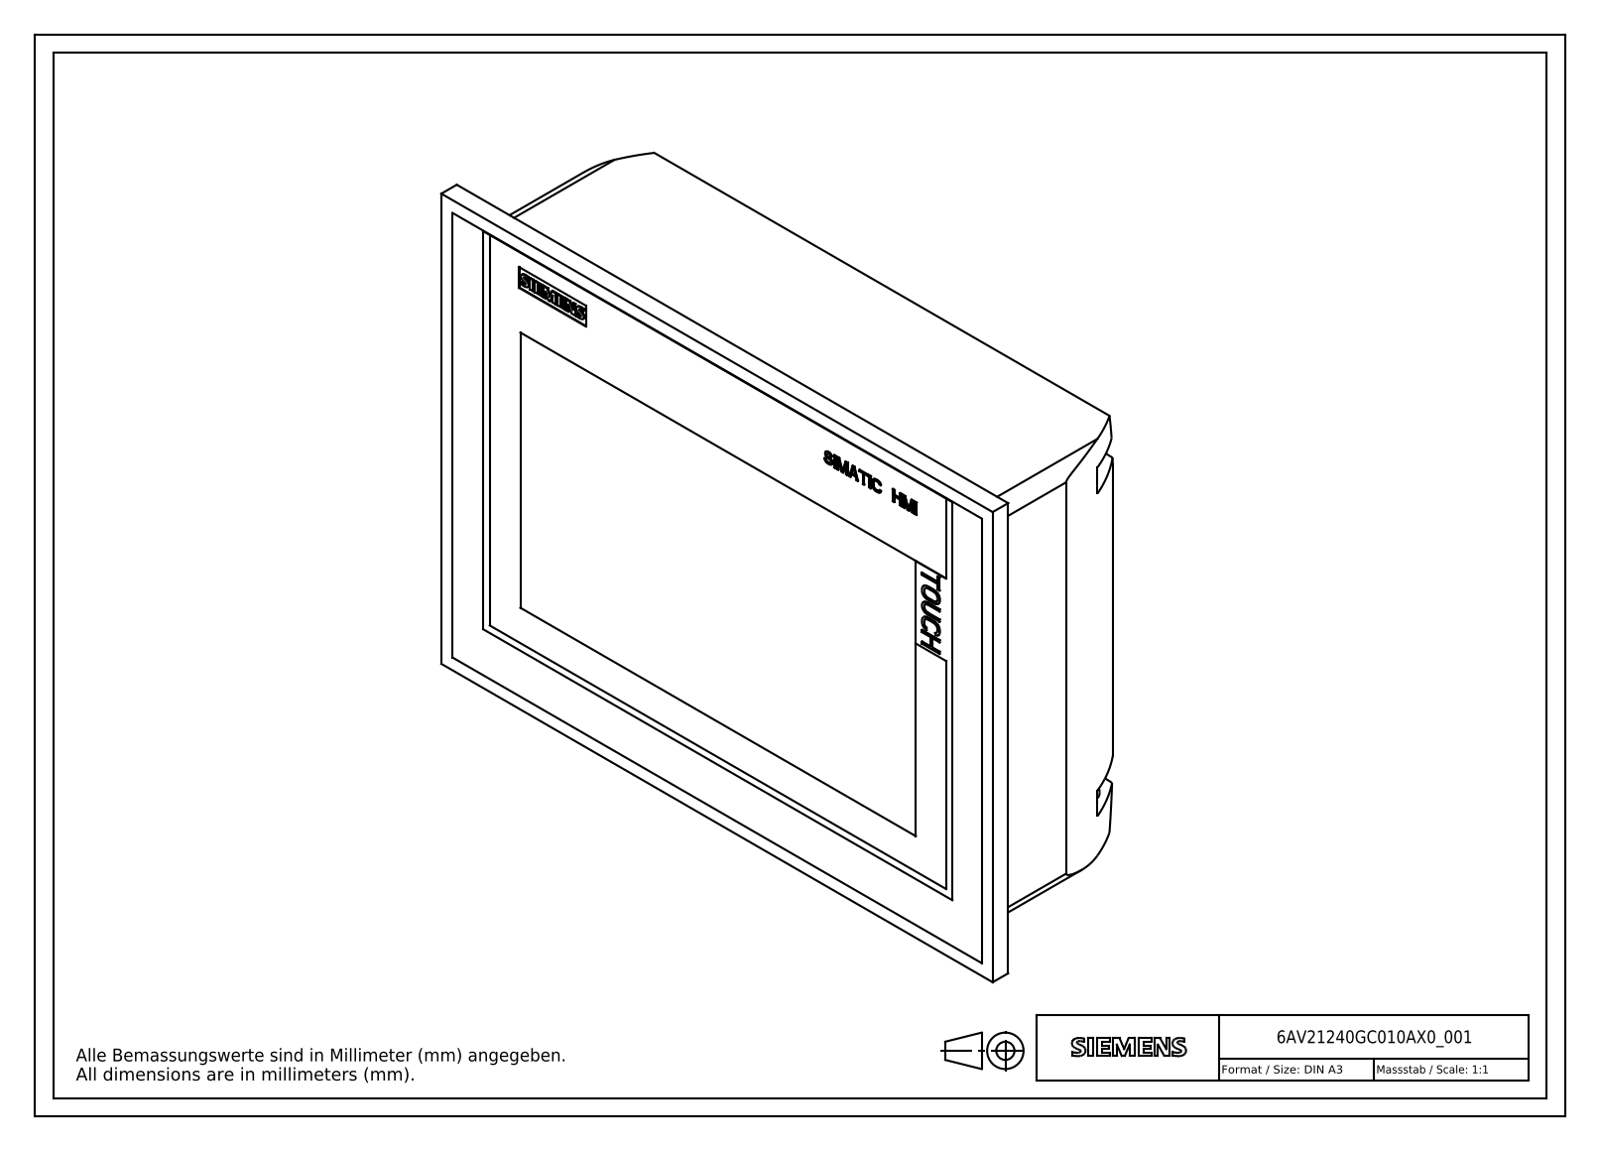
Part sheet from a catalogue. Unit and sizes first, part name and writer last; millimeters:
Units: millimetres
Overall size (bounding box): 214 × 158 × 69.1
Round holes (diameter × count): ⌀0.9 ×9, ⌀2.4 ×2, ⌀3.8 ×2, ⌀8.5 ×2
Round bosses / shafts (diameter × count): ⌀7 ×7, ⌀5.5 ×4, ⌀3 ×2, ⌀0.96 ×2, ⌀0.8 ×2
Partial cylindrical surfaces — rounded edges, fillets, slot ends (radius × count): R0.2 ×65, R0.3 ×24, R0.8 ×24, R0.85 ×6, R0.45 ×4, R1.85 ×4, R2.02 ×4, R3.75 ×4
Main face-to-face distances: 63, 67.92, 4.92, 68.58, 5.58, 0.66, 8, 68.7, 5.7, 0.78
Hole centre spacings: 3.07, 2.76, 4.96, 5.52, 7.42, 8.28, 7.15, 8.44
Volume: 1 784 000 mm³ · Surface area: 204 527 mm²
Bodies: 261 solids, 2725 faces (2250 planar, 200 cylindrical, 275 other)
Part name (STEP PRODUCT): A5E30321192A_001; A5E30291720A_001; A5E30291714A_001; A5E30291710A_001 (+1 more)
STEP written by: SIEMENS UGS NX 6.0 (AUTOMOTIVE_DESIGN)
